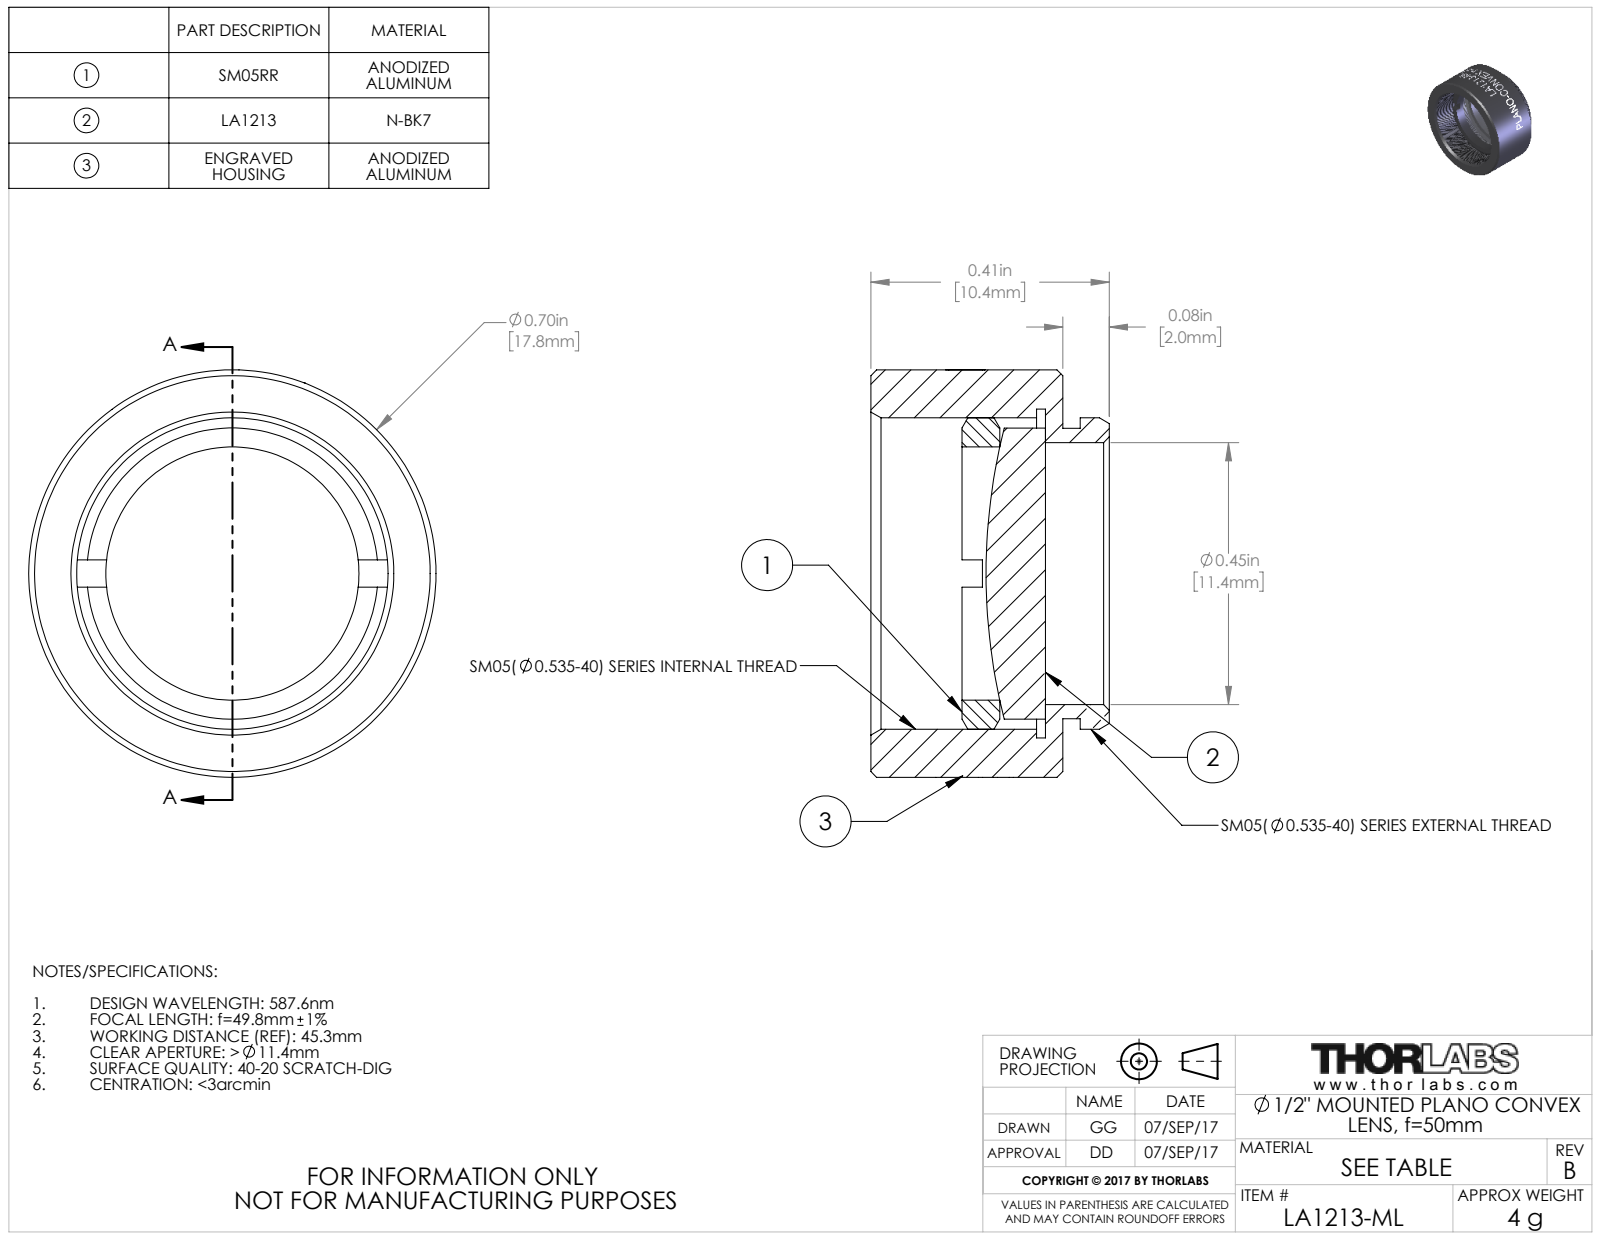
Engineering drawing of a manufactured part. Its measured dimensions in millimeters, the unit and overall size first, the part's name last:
Units: millimetres
Overall size (bounding box): 17.8 × 17.8 × 10.4
Round holes (diameter × count): ⌀11 ×1, ⌀11.4 ×1, ⌀13.6 ×1, ⌀14.4 ×1
Round bosses / shafts (diameter × count): ⌀17.8 ×1, ⌀13.6 ×1, ⌀12.7 ×1, ⌀12.7 ×1
Partial cylindrical surfaces — rounded edges, fillets, slot ends (radius × count): R8.9 ×1
Main face-to-face distances: 0.8, 7.6, 8.4, 2.8, 2, 5.6, 4.4, 3.6, 1.7, 4
Volume: 1 300 mm³ · Surface area: 1 842 mm²
Bodies: 3 solids, 240 faces (94 planar, 71 cylindrical, 75 other)
Part name (STEP PRODUCT): 24398-E0W
STEP written by: SolidWorks 2016 (CONFIG_CONTROL_DESIGN)
